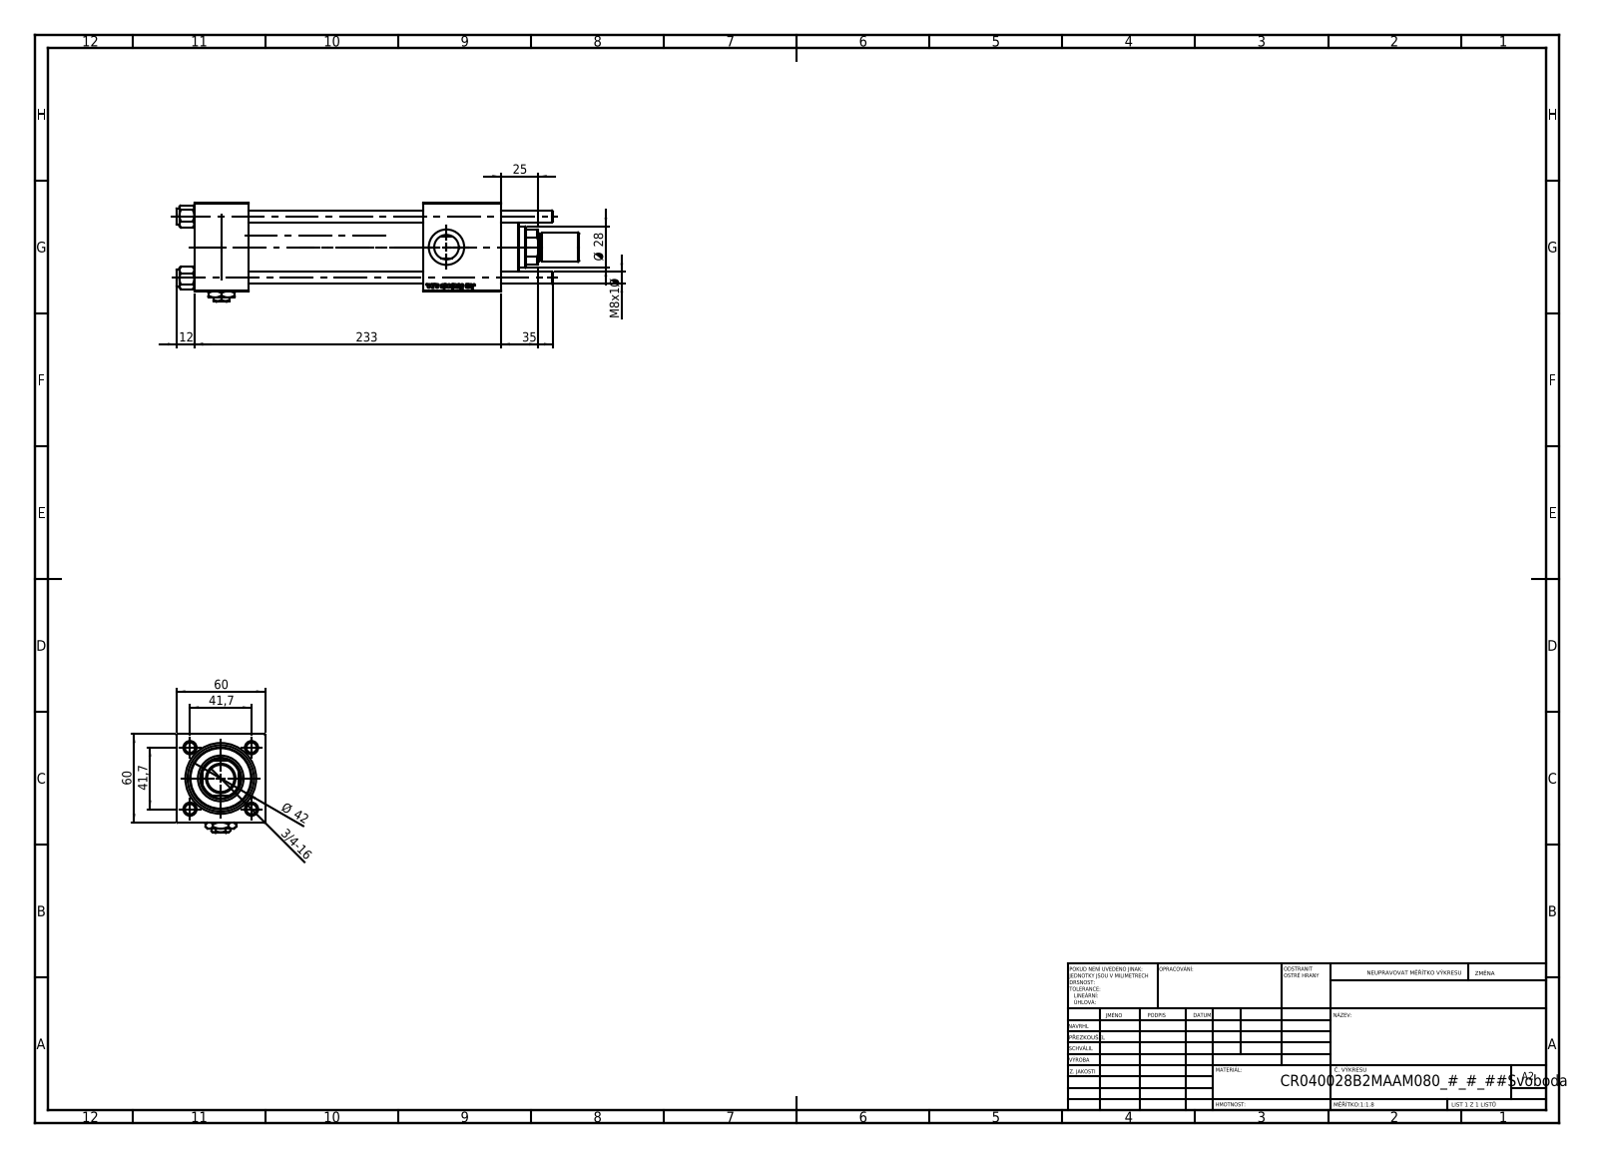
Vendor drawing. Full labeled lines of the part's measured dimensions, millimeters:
Part name (STEP PRODUCT): V215CR_VCP_B; V215_VC_A; ROD_END_AH; V215CR_B-1 (+3 more)
STEP written by: SolidWorks 2019 (CONFIG_CONTROL_DESIGN)
Units: millimetres
Bodies: 13 solids, 1226 faces (460 planar, 90 cylindrical, 676 other)
Overall size (bounding box): 273 × 67 × 60
Volume: 515 494 mm³ · Surface area: 151 662 mm²
Round holes (diameter × count): ⌀8 ×4, ⌀7 ×2, ⌀16.66 ×2, ⌀24 ×2, ⌀16 ×1, ⌀18.5 ×1, ⌀28 ×1, ⌀31 ×1, ⌀40 ×1, ⌀45 ×1
Round bosses / shafts (diameter × count): ⌀11 ×4, ⌀46 ×1, ⌀42 ×1, ⌀20 ×1, ⌀18 ×1
Partial cylindrical surfaces — rounded edges, fillets, slot ends (radius × count): R13.5 ×1
Main face-to-face distances: 60, 37, 155, 118, 53, 179.3, 142.3, 24.3, 208, 171
Hole centre spacings: 29.49, 41.7, 58.97
